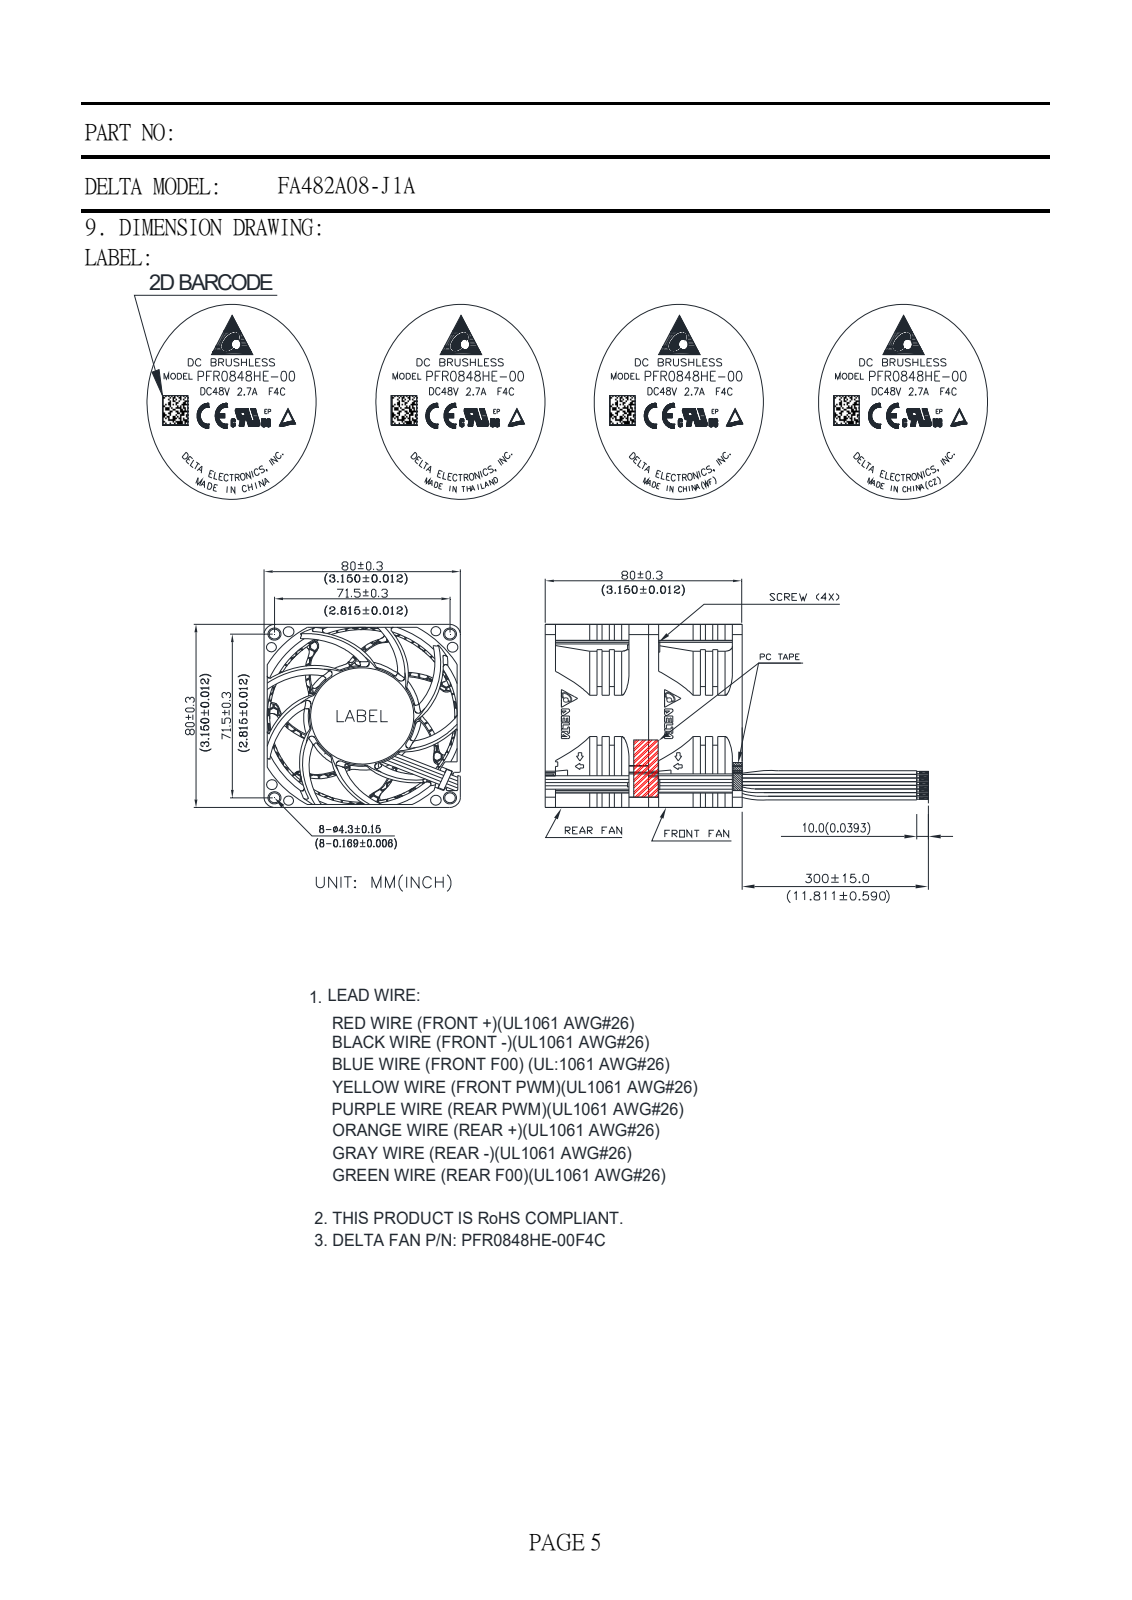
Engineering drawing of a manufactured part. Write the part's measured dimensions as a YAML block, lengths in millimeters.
part_name: "F_FRAME; IMP; R_FRAME; ASM_ASM"
step_written_by: "CREO PARAMETRIC BY PTC INC, 2015080 (CONFIG_CONTROL_DESIGN)"
units: millimeters
bodies: {solids: 3, faces: 1086, planar: 403, cylindrical: 463, other: 220}
overall_size: [80.2, 80, 80]
volume: 200895
surface_area: 93201
round_holes:
  - {diameter: 4.3, count: 8}
  - {diameter: 5.3, count: 4}
  - {diameter: 4, count: 3}
  - {diameter: 77.4, count: 1}
round_bosses_or_shafts:
  - {diameter: 44, count: 1}
partial_cylinders:
  - {radius: 0.5, count: 61}
  - {radius: 1, count: 8}
  - {radius: 61.82, count: 7}
  - {radius: 62.34, count: 7}
  - {radius: 0.3, count: 4}
  - {radius: 4.5, count: 4}
  - {radius: 0.6, count: 1}
  - {radius: 1.5, count: 1}
face_to_face_distances: [42.1, 11.34, 80, 53.44, 30.76, 1.3, 78.7, 77.4, 80.2, 68.86]
hole_center_spacings: [65.76, 5.85, 47.48, 50.56, 67.15, 71.5, 72.78, 97.91]
